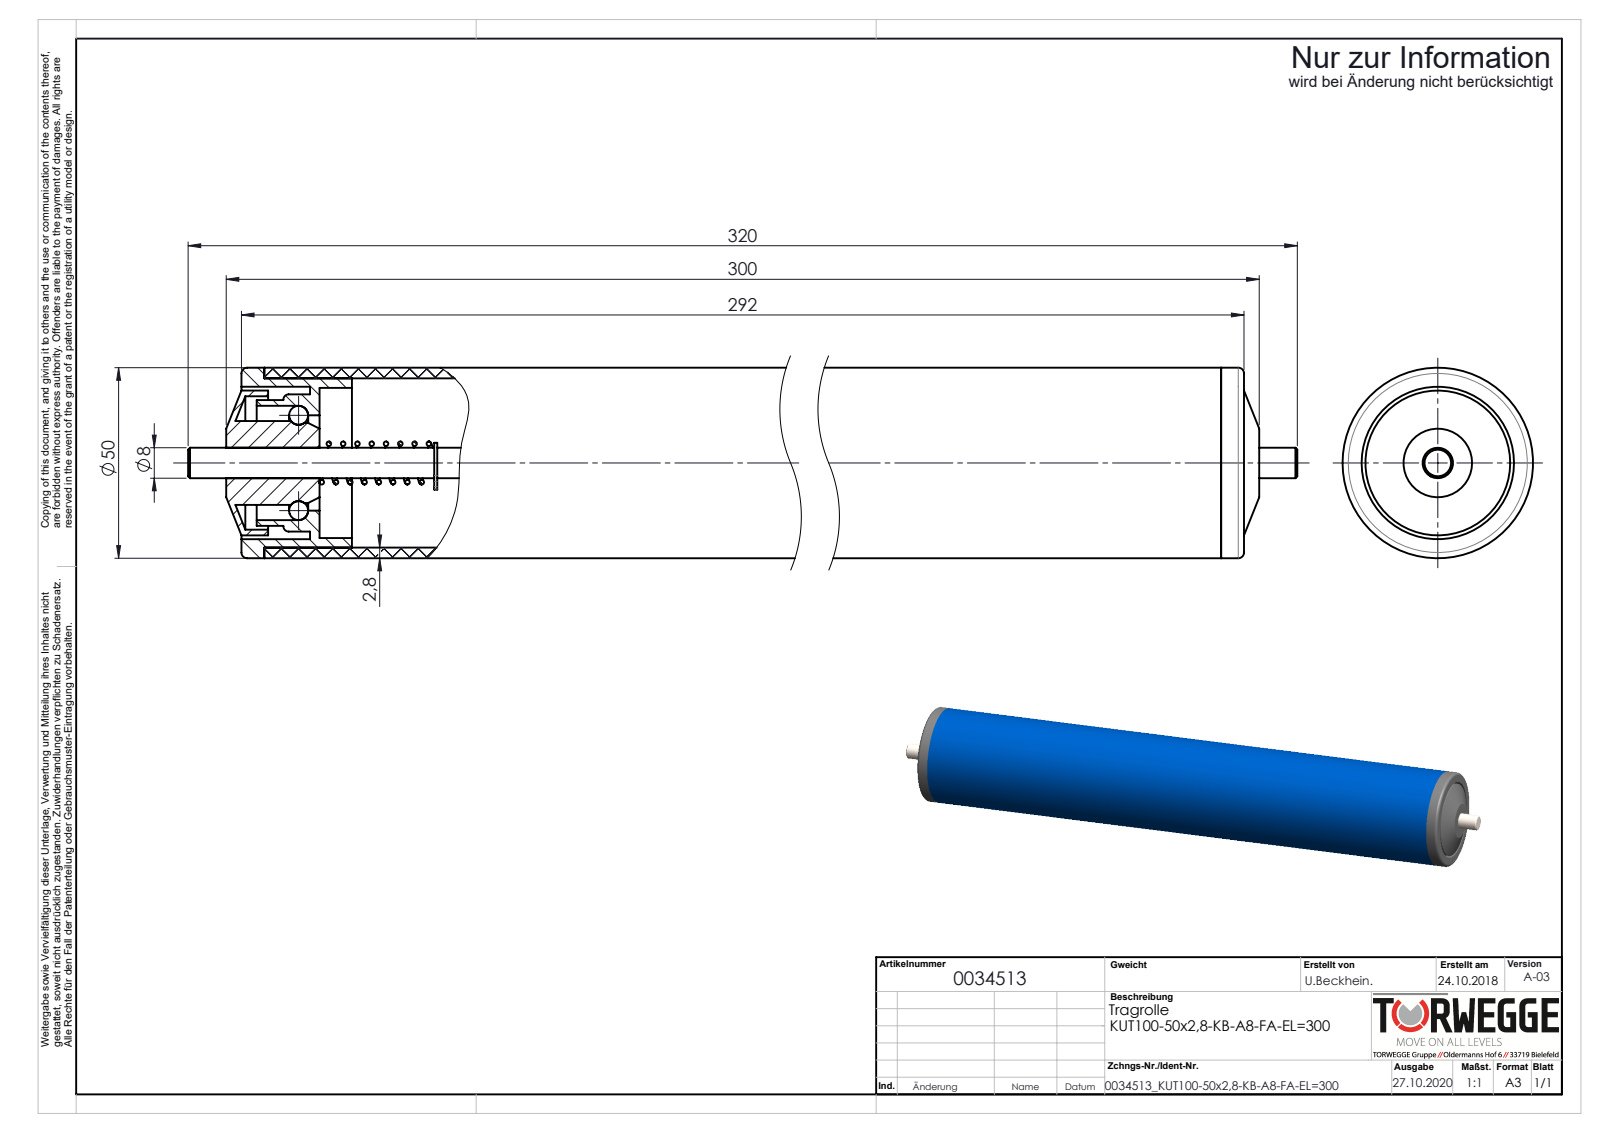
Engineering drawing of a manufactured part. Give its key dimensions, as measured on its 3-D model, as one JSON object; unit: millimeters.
{"part_name": "0034513", "step_written_by": "SolidWorks 2018 (AUTOMOTIVE_DESIGN)", "units": "millimeters", "bodies": {"solids": 11, "faces": 186, "planar": 52, "cylindrical": 88, "other": 46}, "overall_size": [320, 50, 50], "volume_mm3": 188321, "surface_area_mm2": 133602, "round_holes": [[7.6, 1], [8, 1], [25, 1], [30, 1], [35, 1], [39.4, 1], [40, 1]], "round_bosses_or_shafts": [[50, 1], [44.4, 1], [38, 1], [36, 1], [33, 1], [22, 1], [21, 1]], "partial_cylinders_radius": [[0.6, 2], [0.75, 2], [2.45, 2], [4.87, 1], [7, 1]], "face_to_face_distances": [14.5, 265.5, 11, 6, 20.5, 271.5, 286, 251, 280, 292]}
